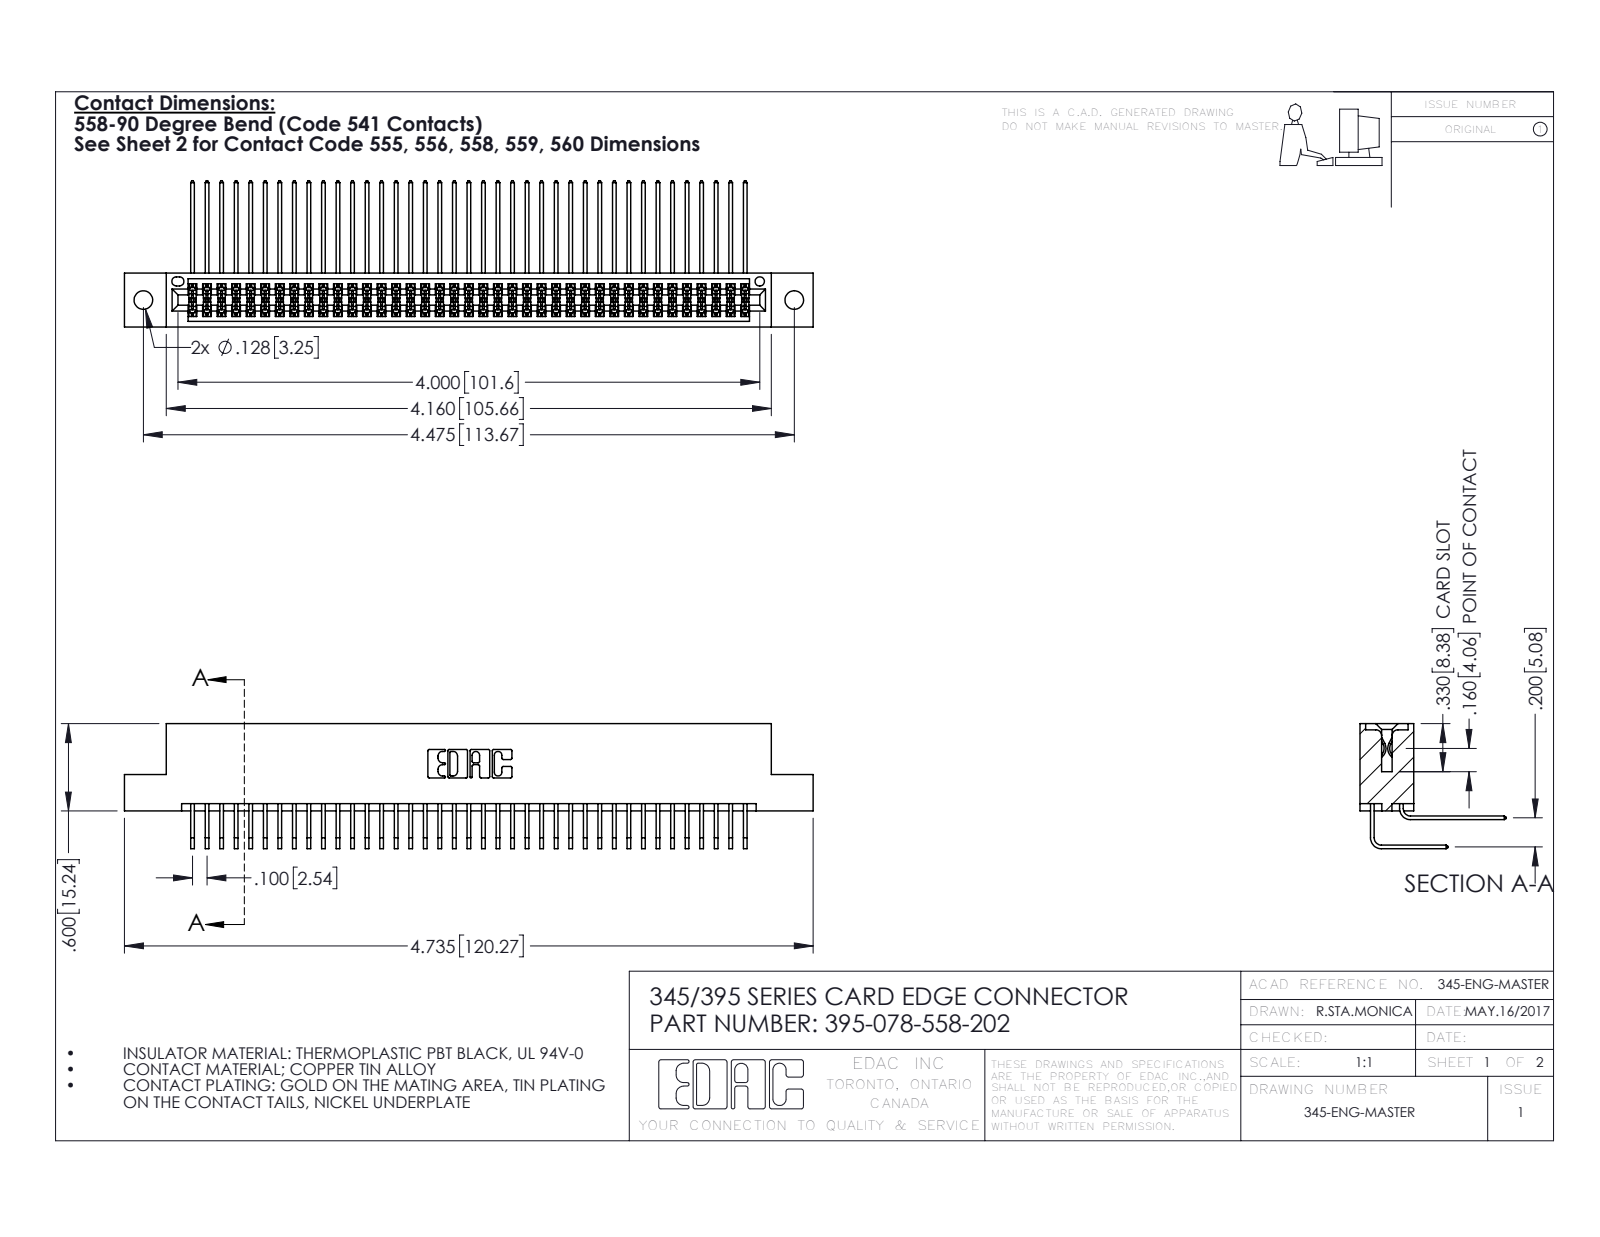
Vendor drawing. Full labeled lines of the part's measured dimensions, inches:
Part name (STEP PRODUCT): 345-292-001_558 Tail - 2; 345-292-001_558 559 Tail - 1; 345 Part_Flush Mounting Lugs - 0.128 Dia; 395-078-558-202
STEP written by: SolidWorks 2016 (CONFIG_CONTROL_DESIGN)
Units: inches
Bodies: 79 solids, 4182 faces (2810 planar, 1372 cylindrical, 0 other)
Overall size (bounding box): 4.735 × 1.005 × 0.859
Volume: 0.736 in³ · Surface area: 30.42 in²
Round holes (diameter × count): ⌀0.128 ×2, ⌀0.064 ×1
Partial cylindrical surfaces — rounded edges, fillets, slot ends (radius × count): R0.006 ×118, R0.01 ×22, R0.007 ×6, R0.031 ×6, R0.026 ×3, R0.014 ×2, R0.019 ×2, R0.022 ×2
Main face-to-face distances: 0.072, 0.298, 0.2, 0.37, 0.098, 0.272, 0.025, 0.225, 0.025, 0.175
Hole centre spacings: 0.27, 4.239, 4.475
